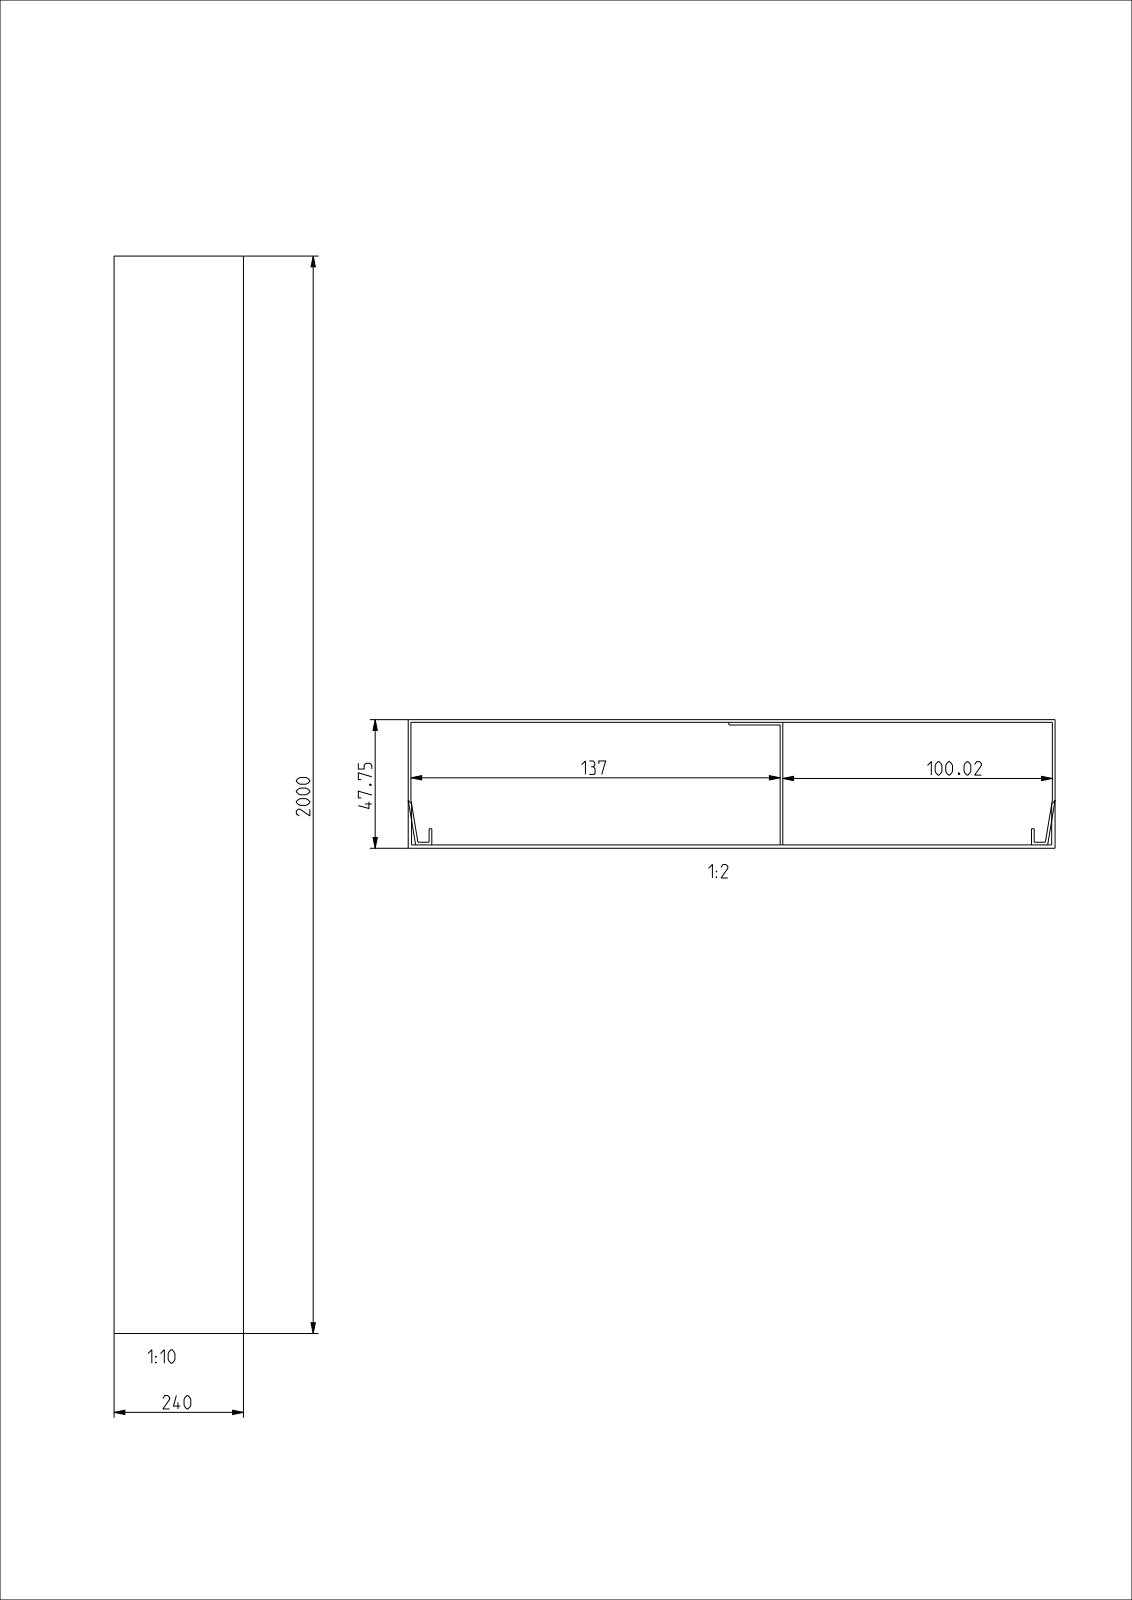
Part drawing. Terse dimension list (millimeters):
name: UK240482KUN_OBERTEIL; UK240482KUN_UNTERTEIL; UK240482KUN_ASM
written by: CREO PARAMETRIC BY PTC INC, 2022024 (AUTOMOTIVE_DESIGN)
unit: mm
bodies: 2 solids, 39 faces (39 planar, 0 cylindrical, 0 other)
size: 2000 × 240 × 47.75
volume: 1 509 000 mm³; area: 2 688 000 mm²
face distances: 1, 1.25, 46.5, 47.75, 45.5, 46.75, 0.98, 239, 240, 138.98
